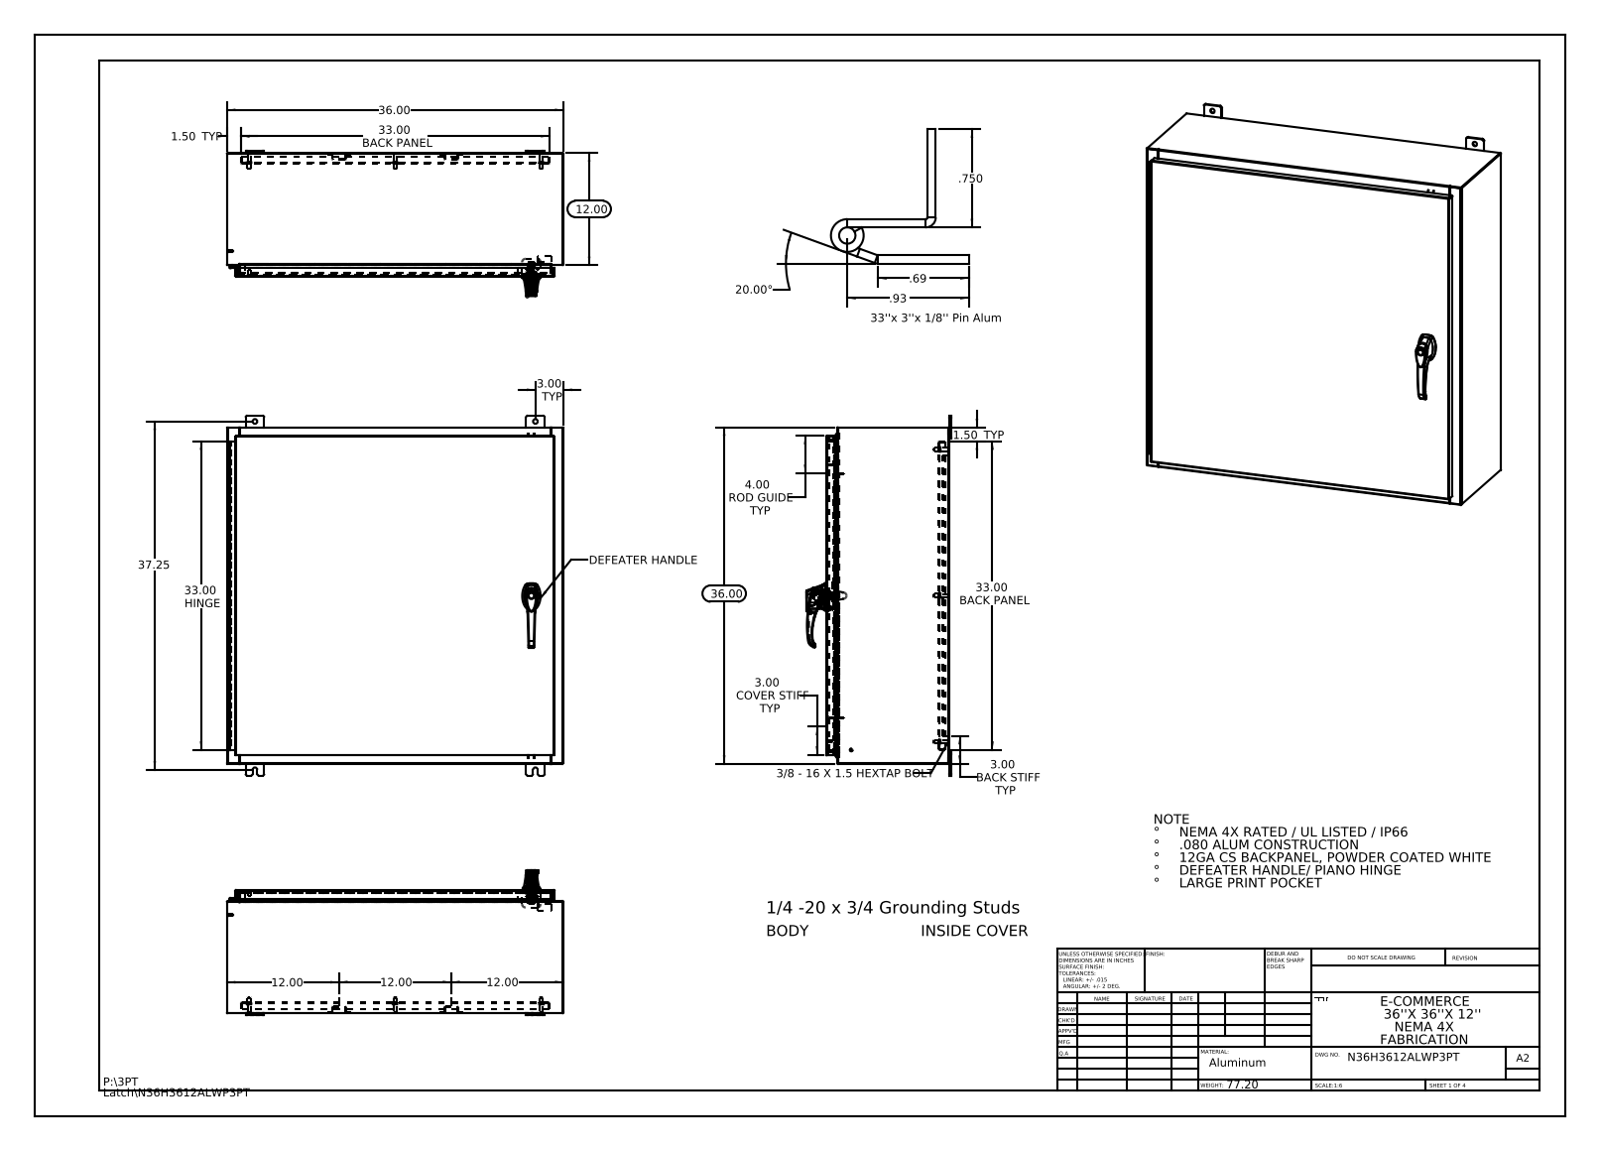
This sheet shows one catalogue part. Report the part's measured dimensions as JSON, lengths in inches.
{"part_name": "10_30 CD Stud; N36H3612ALWP3PT Mounting Feet; NMP-SS-RODGUIDES; N36H3612ALWP3PT 125 Pin Hinge (+8 more)", "step_written_by": "SolidWorks 2013 (CONFIG_CONTROL_DESIGN)", "units": "inches", "bodies": {"solids": 45, "faces": 3022, "planar": 1147, "cylindrical": 1137, "other": 738}, "overall_size": [38.5, 36, 15.495], "volume_in3": 513.8, "surface_area_in2": 12793, "round_holes": [[0.5, 12], [0.25, 10], [0.138, 3], [0.161, 3], [0.079, 2], [0.203, 2], [0.313, 2], [0.437, 2], [0.125, 1], [0.125, 1], [0.197, 1], [0.276, 1]], "round_bosses_or_shafts": [[0.625, 8], [0.375, 8], [0.33, 8], [0.157, 4], [0.14, 4], [0.315, 3], [0.236, 3], [1.181, 1]], "partial_cylinders_radius": [[0.118, 37], [0.013, 34], [0.006, 33], [0.088, 28], [0.19, 24], [0.039, 15], [0.028, 12], [0.008, 6]], "face_to_face_distances": [0.075, 13.126, 35.925, 13.051, 13.201, 0.104, 1, 12.126, 1.075, 12.051], "hole_center_spacings": [15.625, 11.363, 13.669, 22.097, 34.939, 34.939, 31.25, 31.25]}
